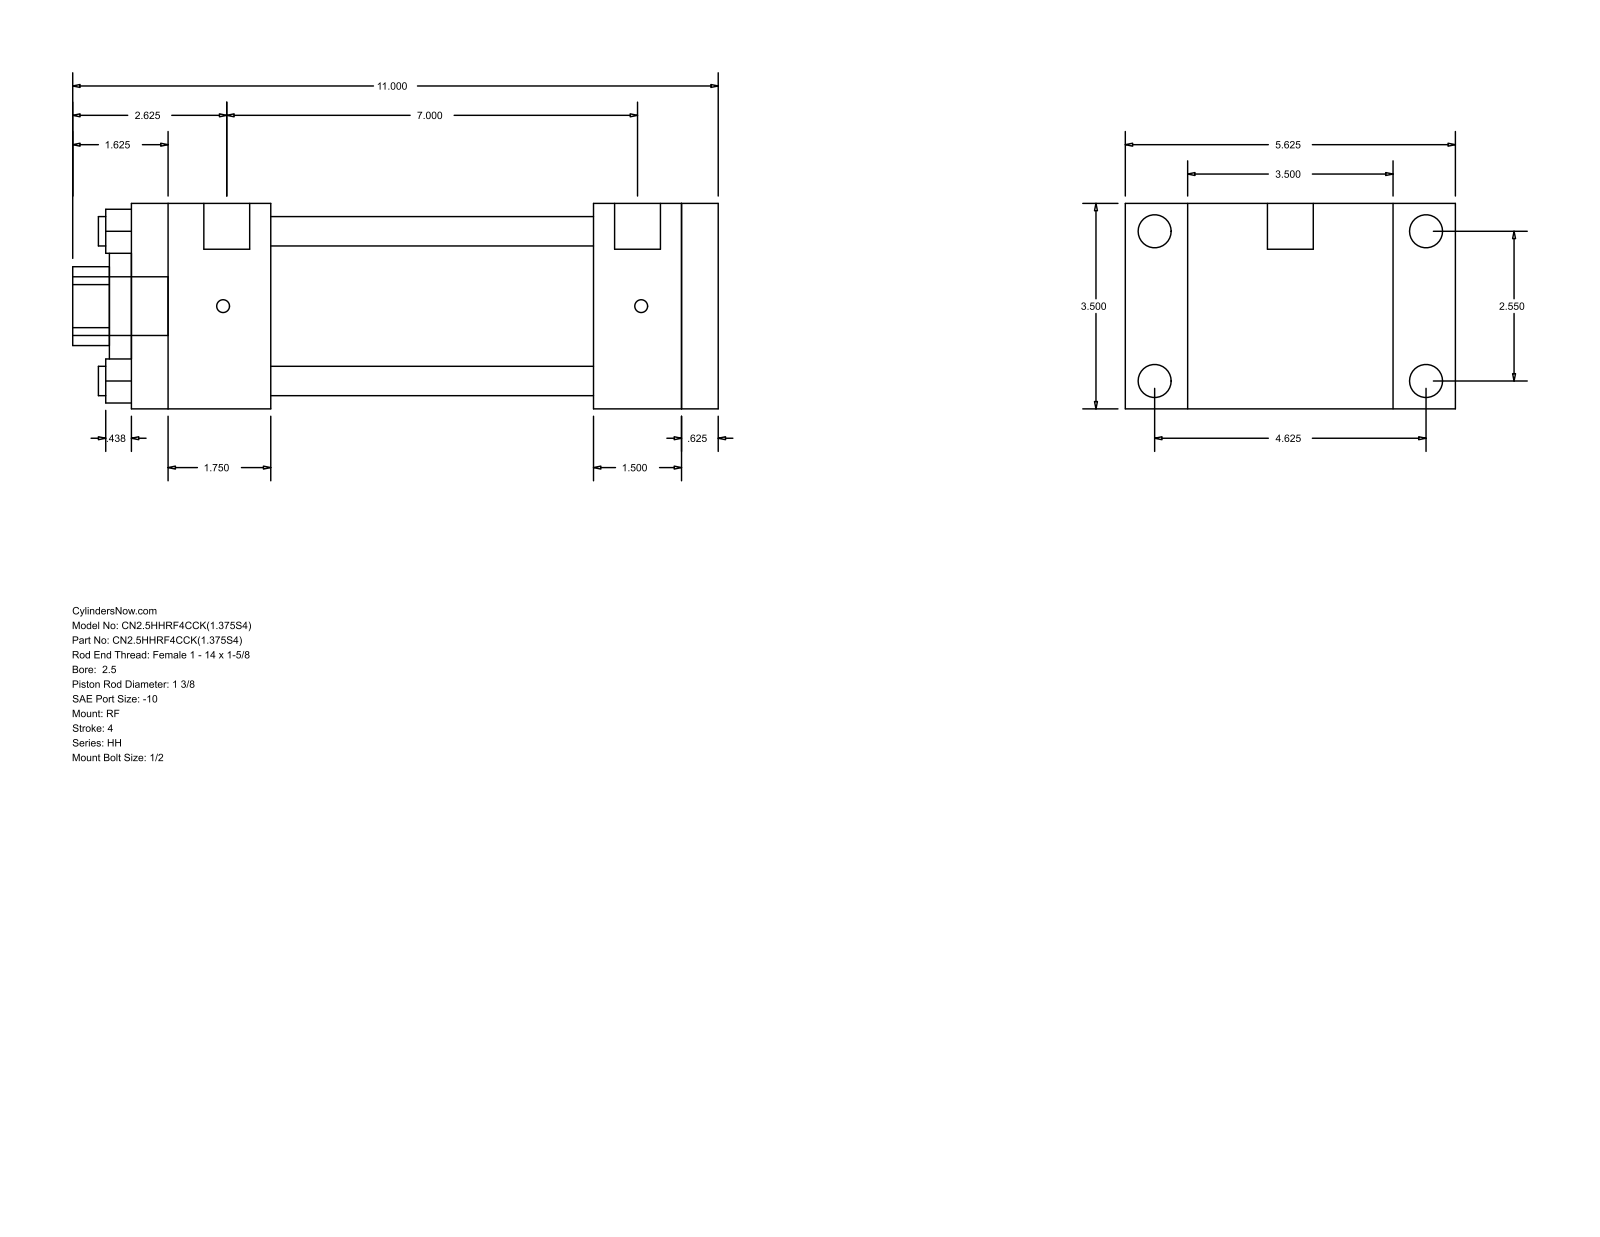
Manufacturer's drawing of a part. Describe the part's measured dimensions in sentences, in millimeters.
The part is named "HH_RF__0250_1.375". Its 3-D file was written by "GSSL Pune (CONFIG_CONTROL_DESIGN)". It is 0 solids with 92 faces: 64 planar, 28 cylindrical and 0 other. Overall it measures 279.4 by 142.88 by 88.9 millimeters. Round holes: 4 of diameter 12.7, 1 of diameter 34.92, 1 of diameter 50.8, 1 of diameter 73.03. Round bosses or shafts: 4 of diameter 14.3, 4 of diameter 5.56, 2 of diameter 19.84, 1 of diameter 25.4. Partial cylindrical surfaces (rounded edges, fillets, slot ends): 1 of radius 17.06. The main face-to-face distances are 88.9, 254, 15.88, 238.12, 60.32, 177.8, 193.68, 200.03, 139.71, 38.09. The hole center spacings are 45.79, 64.76, 91.58.
